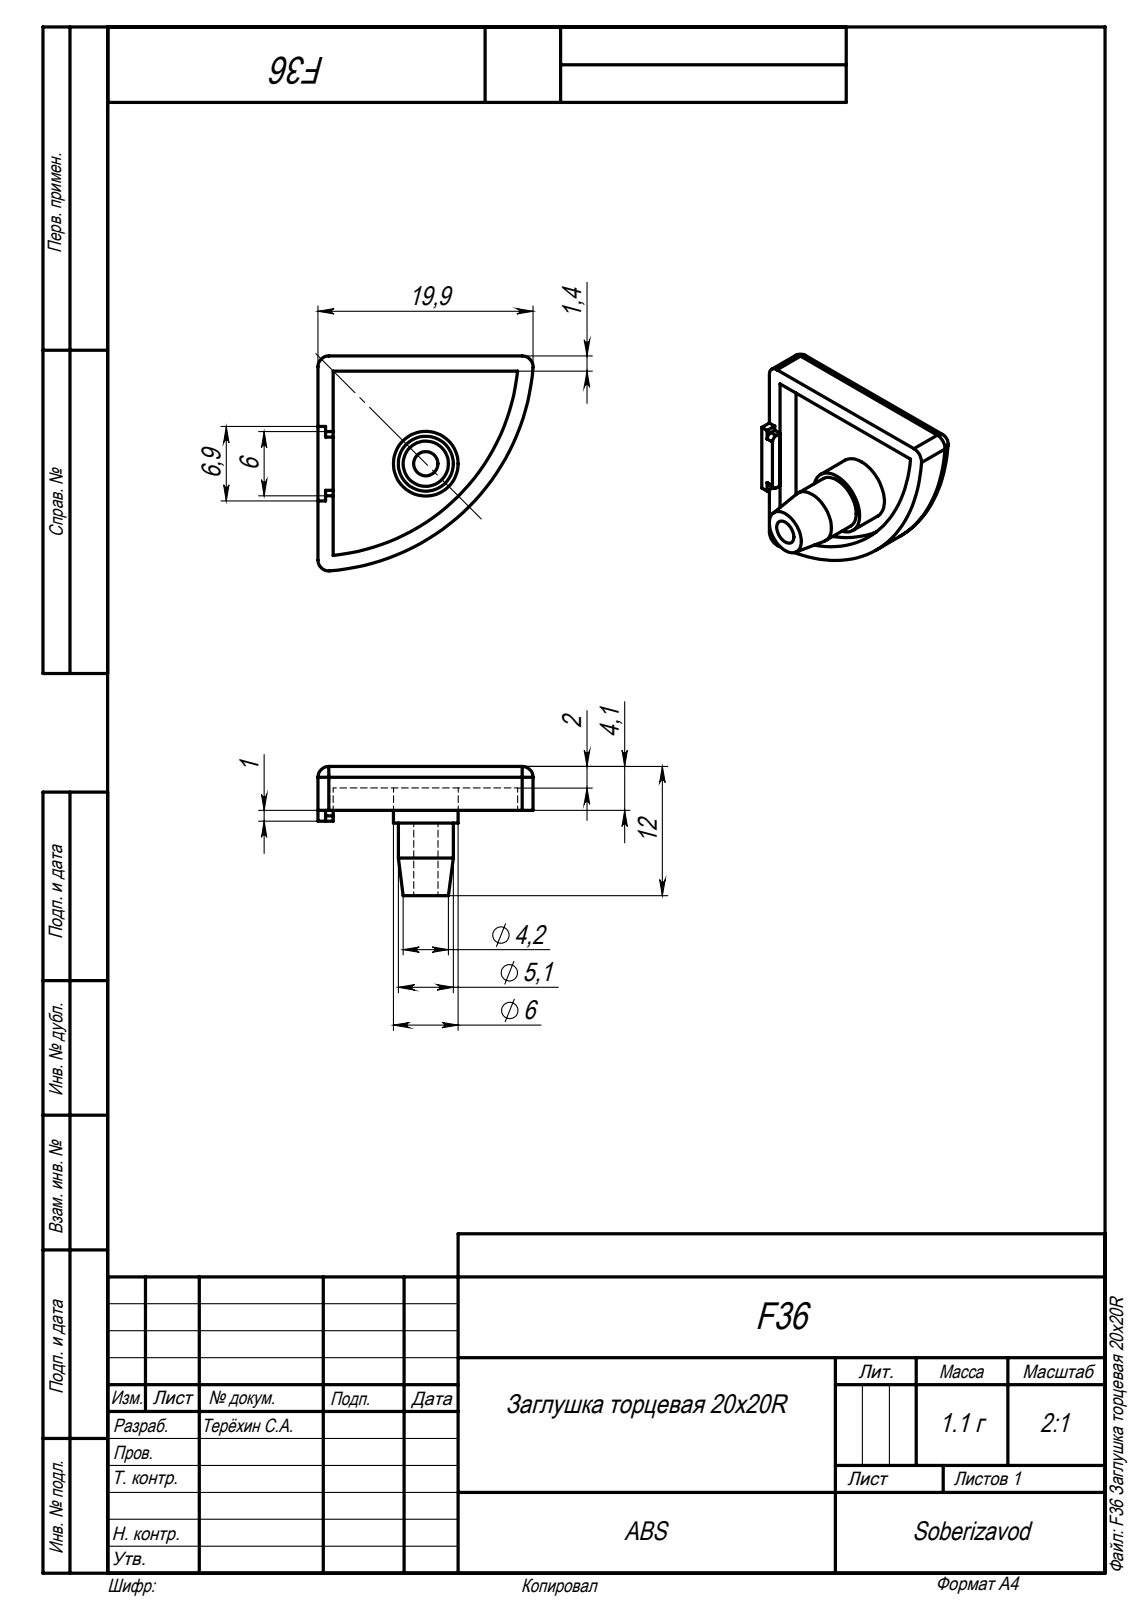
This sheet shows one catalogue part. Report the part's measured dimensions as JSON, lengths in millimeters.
{"step_written_by": "SolidWorks 2018 (AUTOMOTIVE_DESIGN)", "units": "millimeters", "bodies": {"solids": 1, "faces": 39, "planar": 17, "cylindrical": 15, "other": 7}, "overall_size": [19.95, 19.95, 12], "volume_mm3": 984, "surface_area_mm2": 1219, "round_holes": [[2.25, 1]], "round_bosses_or_shafts": [[6, 1], [4.84, 1]], "partial_cylinders_radius": [[1, 5], [0.5, 2], [19.1, 1], [20.5, 1]], "face_to_face_distances": [2, 4.08, 2.08, 1.4, 5.25, 3.25, 1.17, 12, 10, 7.92]}
